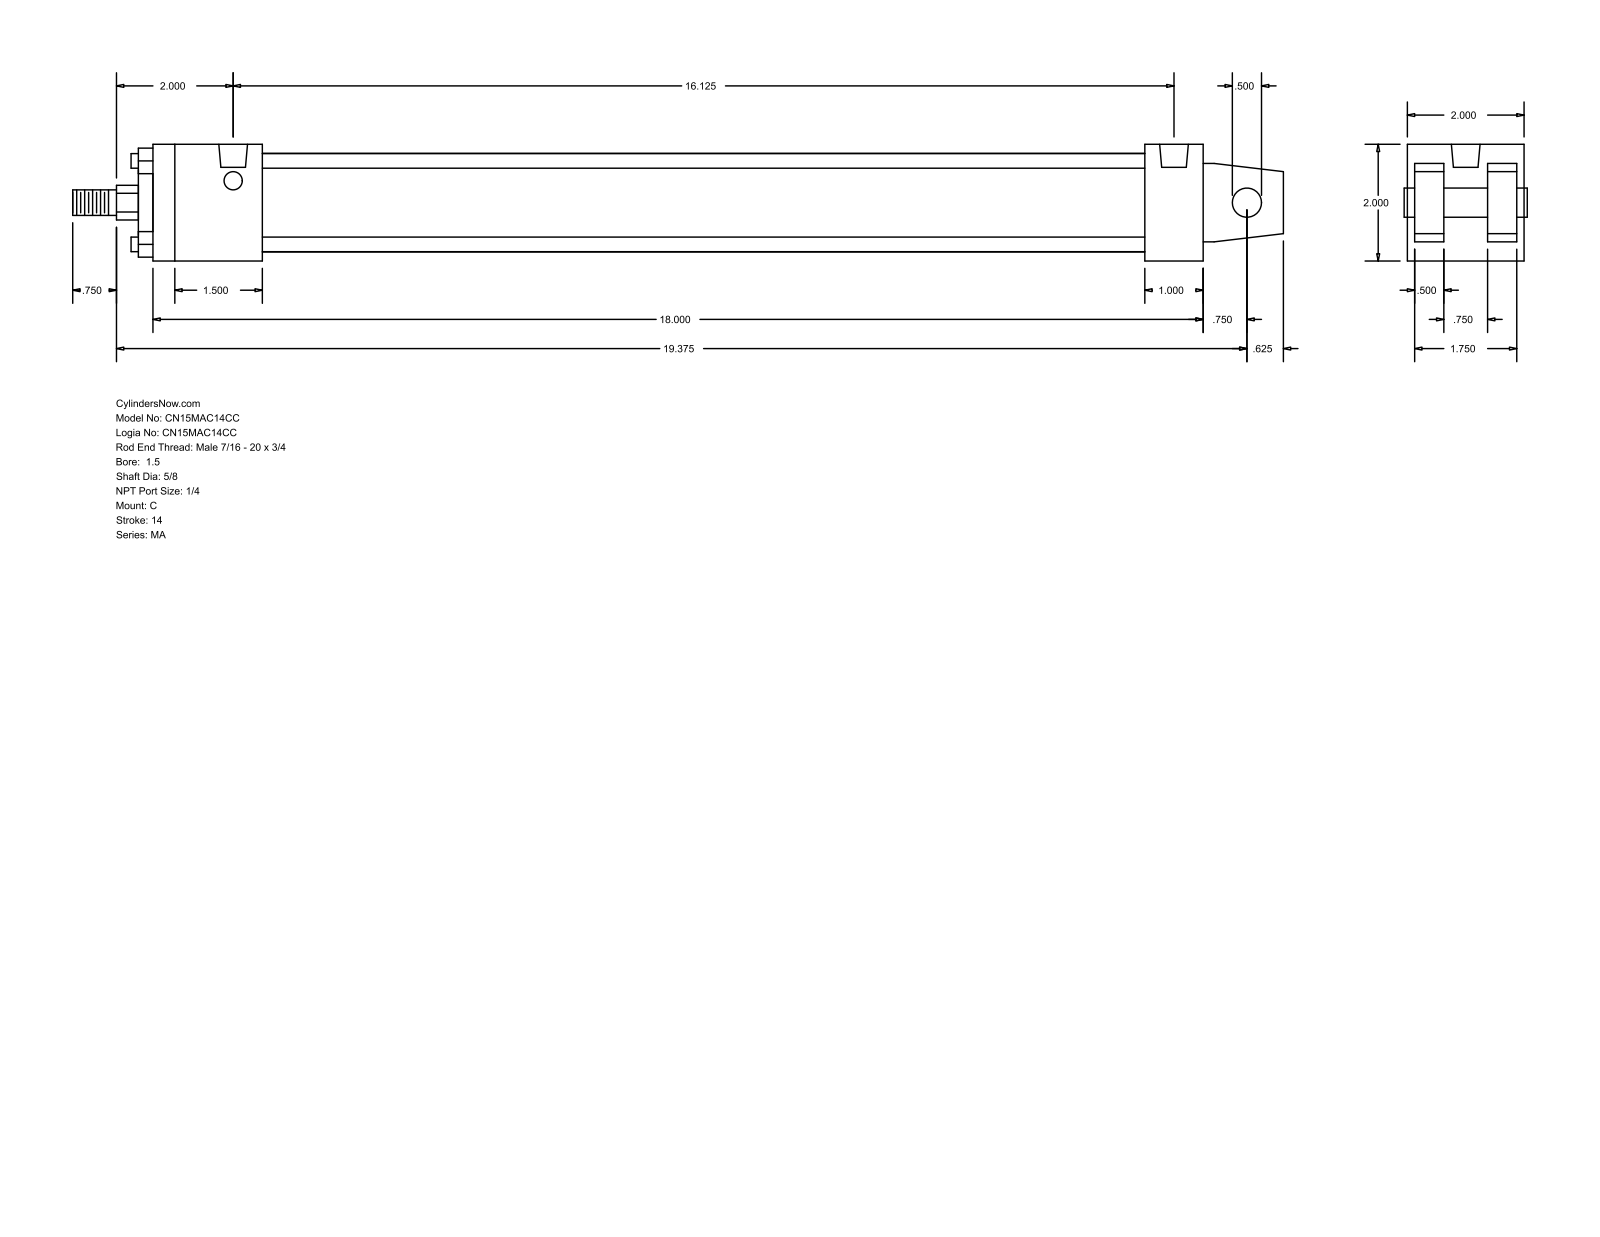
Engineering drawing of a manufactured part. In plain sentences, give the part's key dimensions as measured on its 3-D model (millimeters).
The part is named "MA_C__0150_0.625". Its 3-D file was written by "GSSL Pune (CONFIG_CONTROL_DESIGN)". It is 0 solids with 103 faces: 76 planar, 27 cylindrical and 0 other. Overall it measures 527.05 by 50.8 by 50.8 millimeters. Round holes: 4 of diameter 7.94, 2 of diameter 12.49. Round bosses or shafts: 4 of diameter 6.35, 1 of diameter 42.93, 1 of diameter 28.57, 1 of diameter 15.88, 1 of diameter 12.7, 1 of diameter 11.11. Partial cylindrical surfaces (rounded edges, fillets, slot ends): 1 of radius 7.54. The main face-to-face distances are 50.8, 34.93, 12.7, 15.87, 3.17, 47.63, 31.76, 457.19, 431.8, 25.39. The hole center spacings are 409.58.
